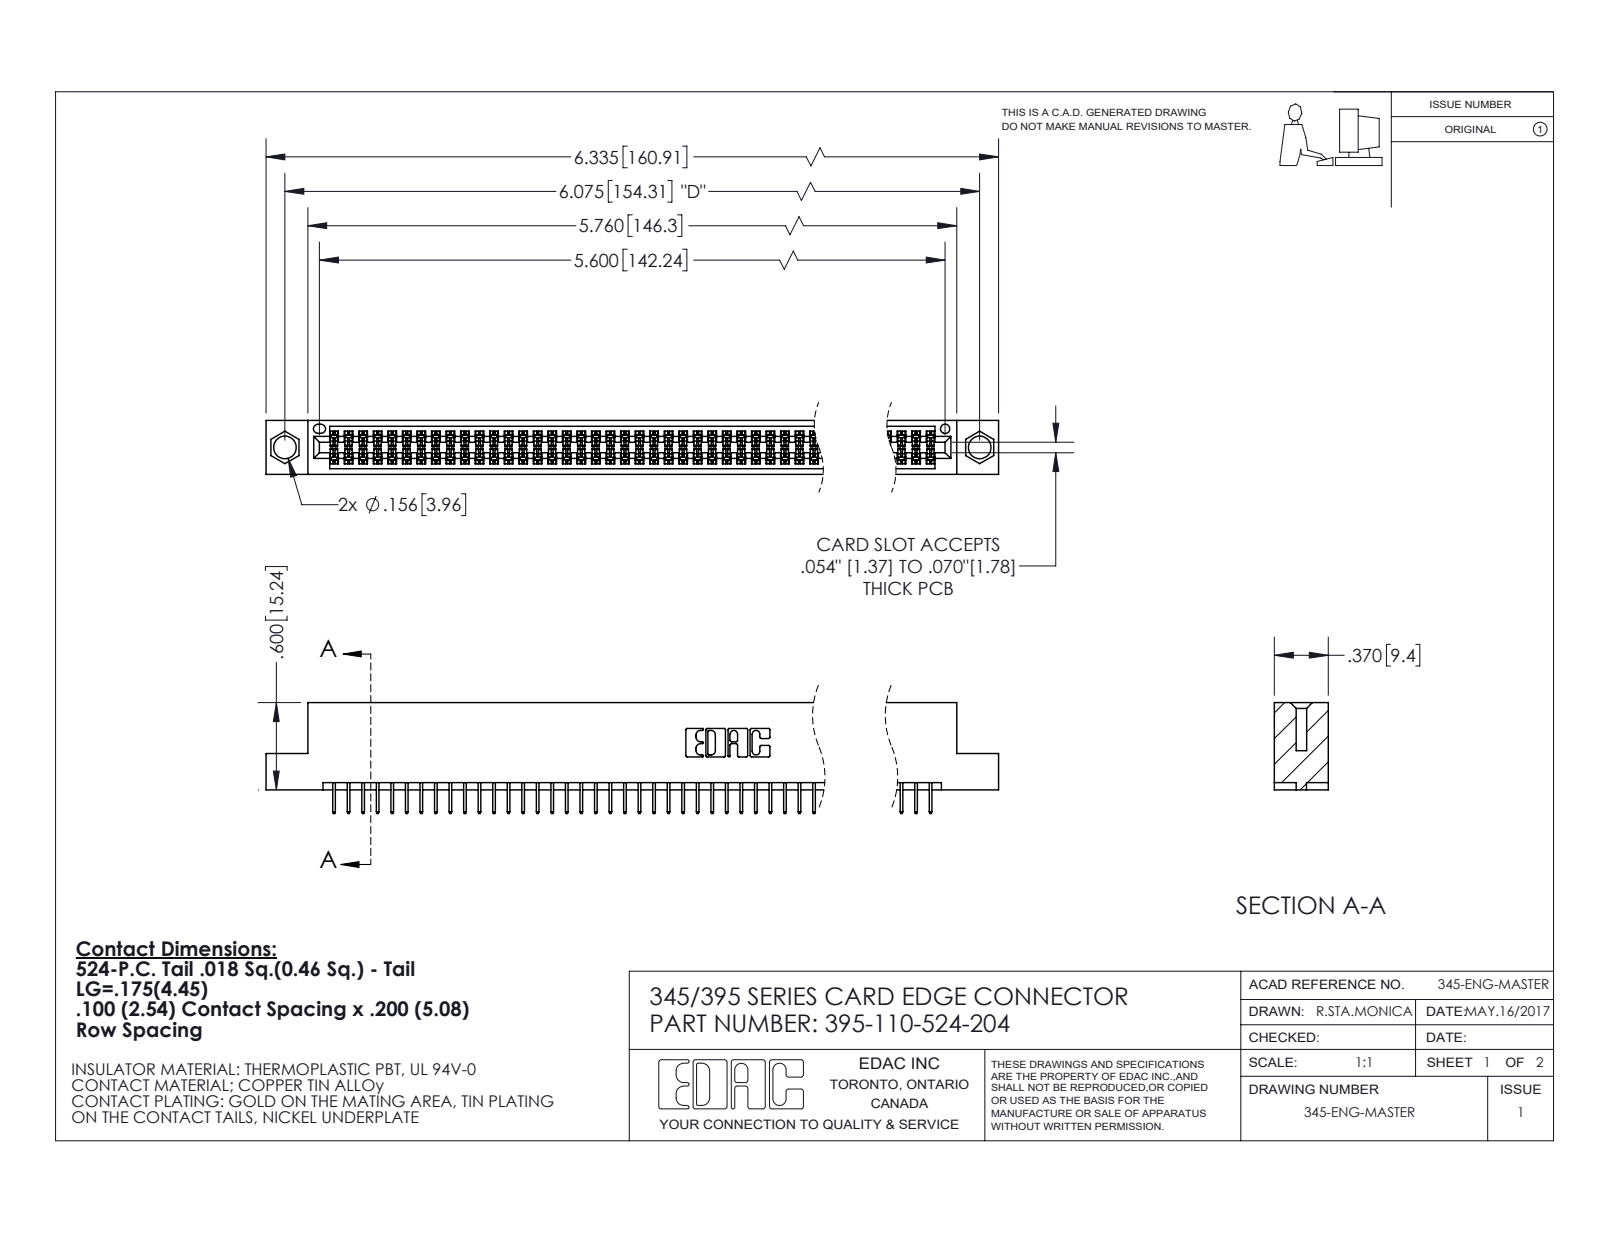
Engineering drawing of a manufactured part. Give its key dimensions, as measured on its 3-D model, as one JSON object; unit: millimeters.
{"part_name": "345-292-001_345-293-124; 345 Part_Flush Mounting Lugs - 0.156 Dia-TI; 395-110-524-204", "step_written_by": "SolidWorks 2020 (CONFIG_CONTROL_DESIGN)", "units": "millimeters", "bodies": {"solids": 111, "faces": 6080, "planar": 4384, "cylindrical": 1696, "other": 0}, "overall_size": [160.9, 19.4, 9.4], "volume_mm3": 15500, "surface_area_mm2": 22540, "round_holes": [[4, 2], [1.6, 1]], "partial_cylinders_radius": [[0.2, 166], [0.3, 22], [0.2, 6], [0.8, 6], [0.7, 3], [0.4, 2], [0.5, 2], [0.6, 2]], "face_to_face_distances": [1.8, 7.6, 5.1, 9.4, 2.5, 6.9, 0.6, 5.7, 1.8, 4.4], "hole_center_spacings": [6.9, 148.3, 154.3]}
